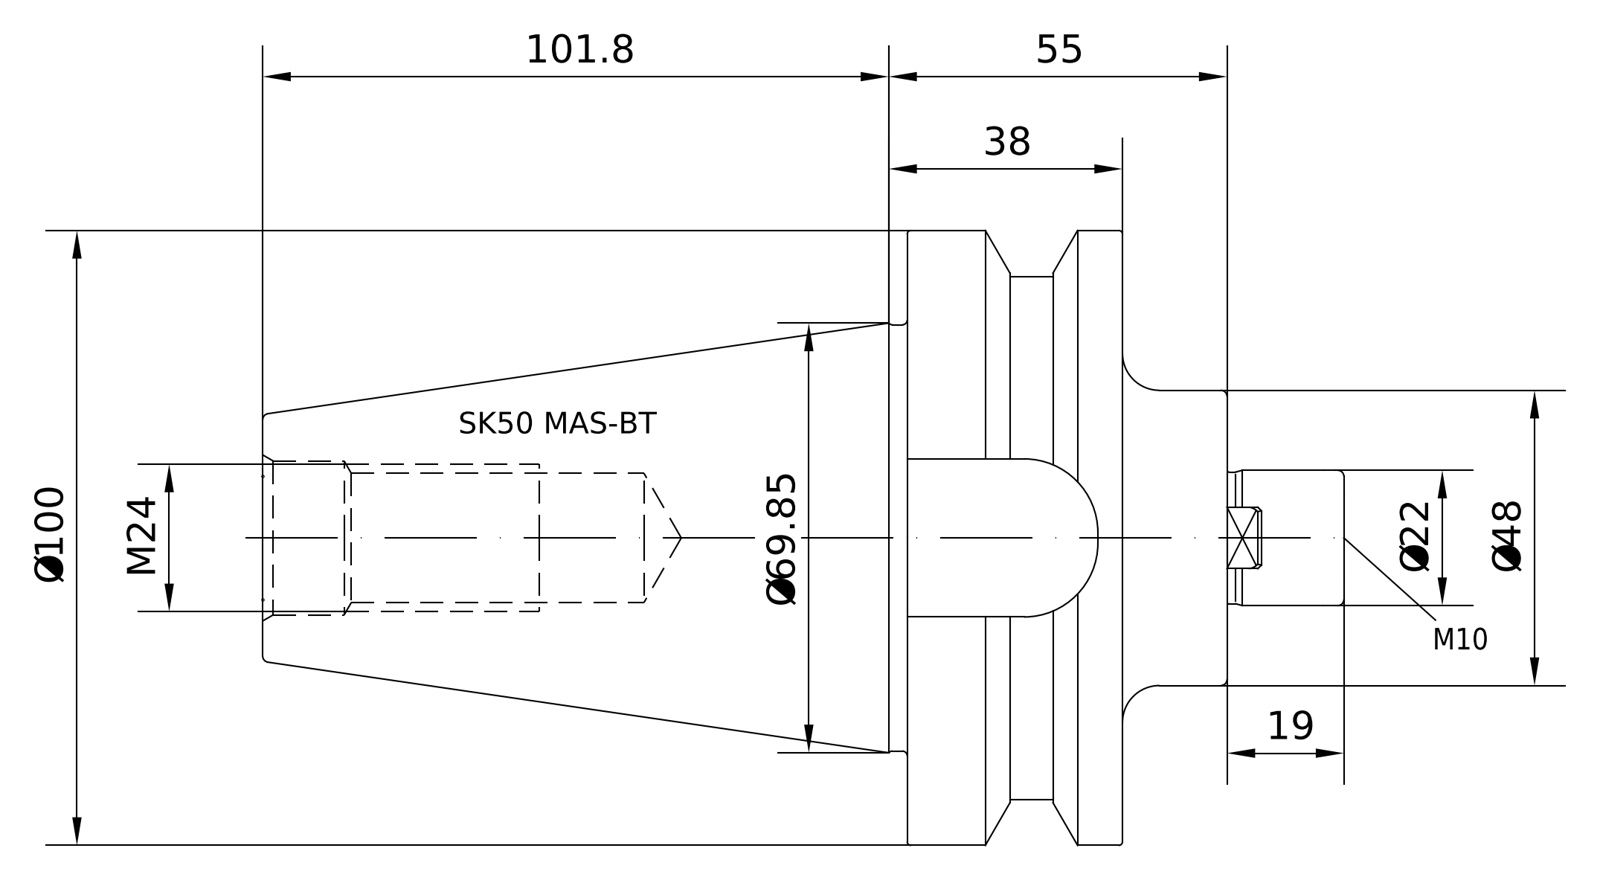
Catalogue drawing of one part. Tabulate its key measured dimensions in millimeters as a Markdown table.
| quantity | value |
| --- | --- |
| part name | 50-550-22 |
| STEP written by | PRO/ENGINEER BY PARAMETRIC TECHNOLOGY CORPORATION, 2010430 (CONFIG_CONTROL_DESIGN) |
| units | millimeters |
| bodies | 1 solid, 113 faces (37 planar, 26 cylindrical, 50 other) |
| overall size | 175.8 × 99.97 × 99.97 |
| volume | 506 585 mm³ |
| surface area | 57 228 mm² |
| round holes (diameter × count) | 8.5 × 1, 10 × 1, 20.75 × 1, 25.02 × 1, 25.7 × 1 |
| round bosses / shafts (diameter × count) | 99.97 × 1, 84.75 × 1, 69.15 × 1, 48 × 1, 24.01 × 1, 22 × 1 |
| partial cylindrical surfaces (radius × count) | 12.9 × 1 |
| main face-to-face distances | 35, 52, 17, 70.4, 104.8, 139.8, 156.8, 25.8, 175.8, 71 |
